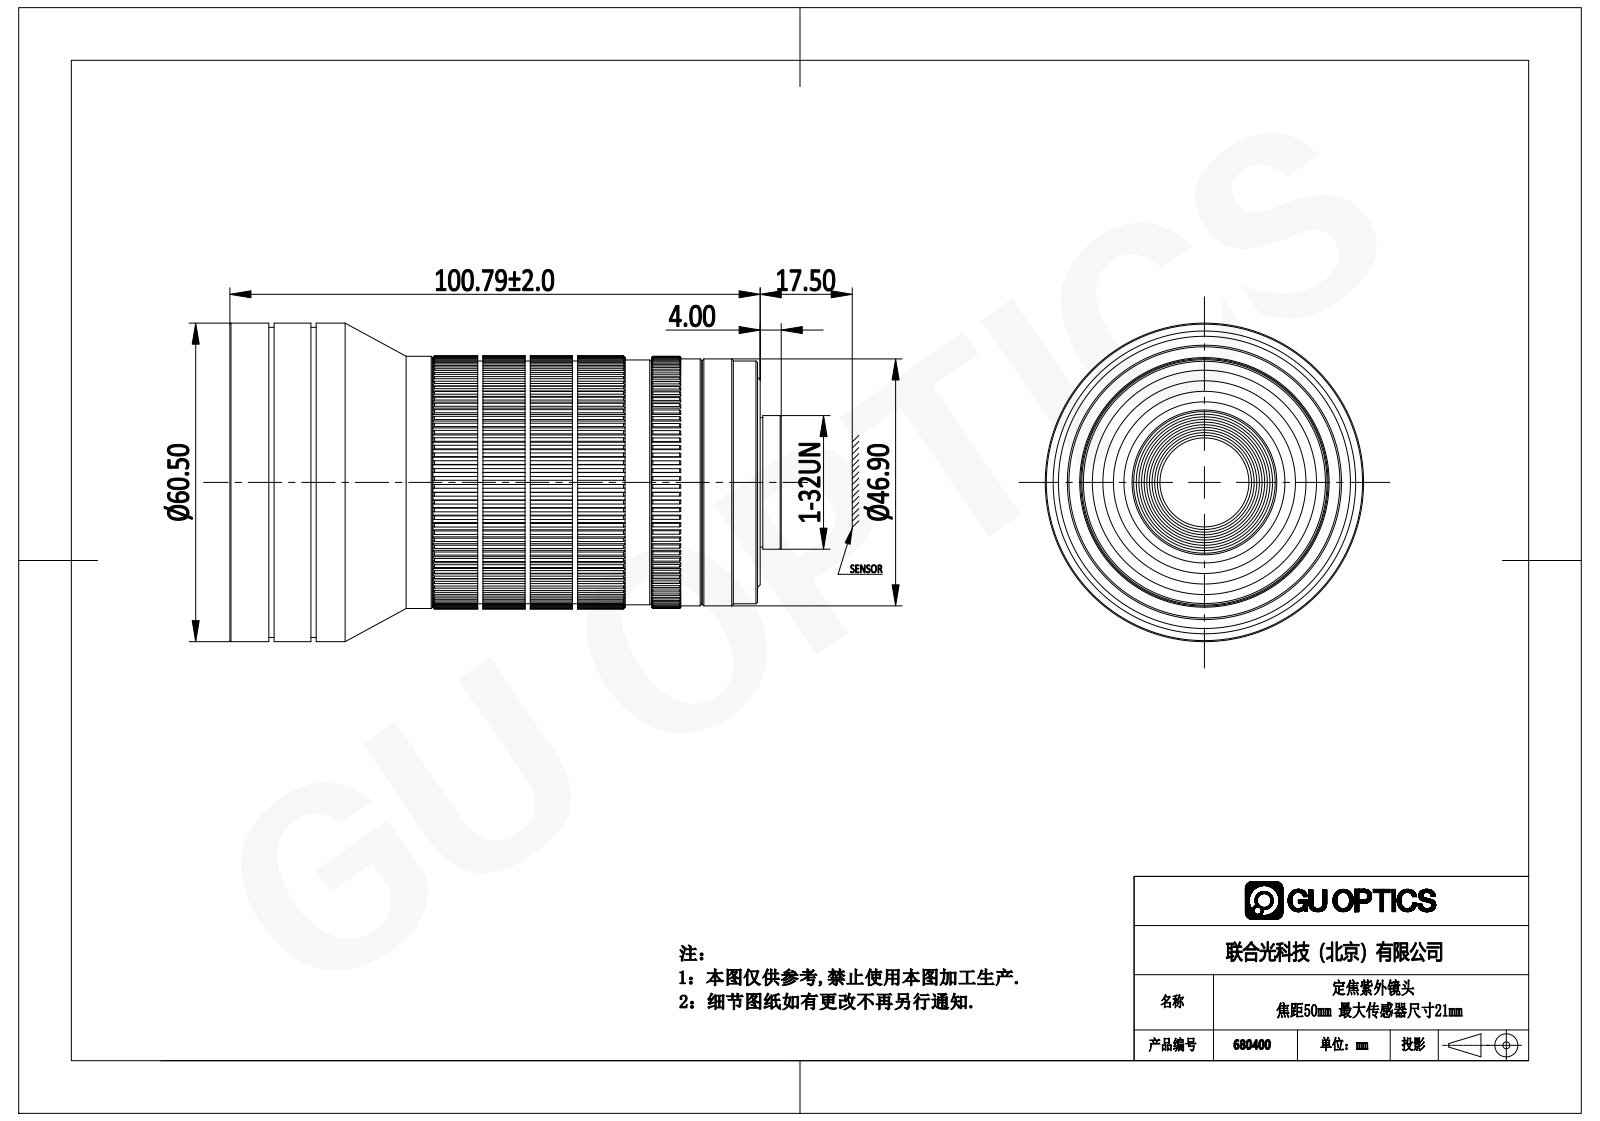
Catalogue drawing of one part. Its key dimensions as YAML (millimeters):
part_name: "BCU5012-10MP"
step_written_by: "PRO/ENGINEER BY PARAMETRIC TECHNOLOGY CORPORATION, 2013430 (CONFIG_CONTROL_DESIGN)"
units: millimeters
bodies: {solids: 1, faces: 2699, planar: 1653, cylindrical: 606, other: 440}
overall_size: [104.79, 60.5, 60.5]
volume: 179260
surface_area: 33511
round_holes:
  - {diameter: 14.8, count: 1}
  - {diameter: 15.2, count: 1}
  - {diameter: 15.6, count: 1}
  - {diameter: 16, count: 1}
  - {diameter: 16.4, count: 1}
  - {diameter: 16.8, count: 1}
  - {diameter: 16.9, count: 1}
  - {diameter: 17.9, count: 1}
  - {diameter: 18.3, count: 1}
  - {diameter: 18.9, count: 1}
  - {diameter: 18.9, count: 1}
  - {diameter: 19.9, count: 1}
round_bosses_or_shafts:
  - {diameter: 60.5, count: 1}
  - {diameter: 58.9, count: 1}
  - {diameter: 55.5, count: 1}
  - {diameter: 47.9, count: 1}
  - {diameter: 46.9, count: 1}
  - {diameter: 46.6, count: 1}
  - {diameter: 46.5, count: 1}
  - {diameter: 46.3, count: 1}
partial_cylinders:
  - {radius: 23.95, count: 1}
  - {radius: 24.05, count: 1}
face_to_face_distances: [0.8, 23.05, 23.85, 23.06, 23.86, 46.9, 23.04, 23.84, 0.82, 0.5]
